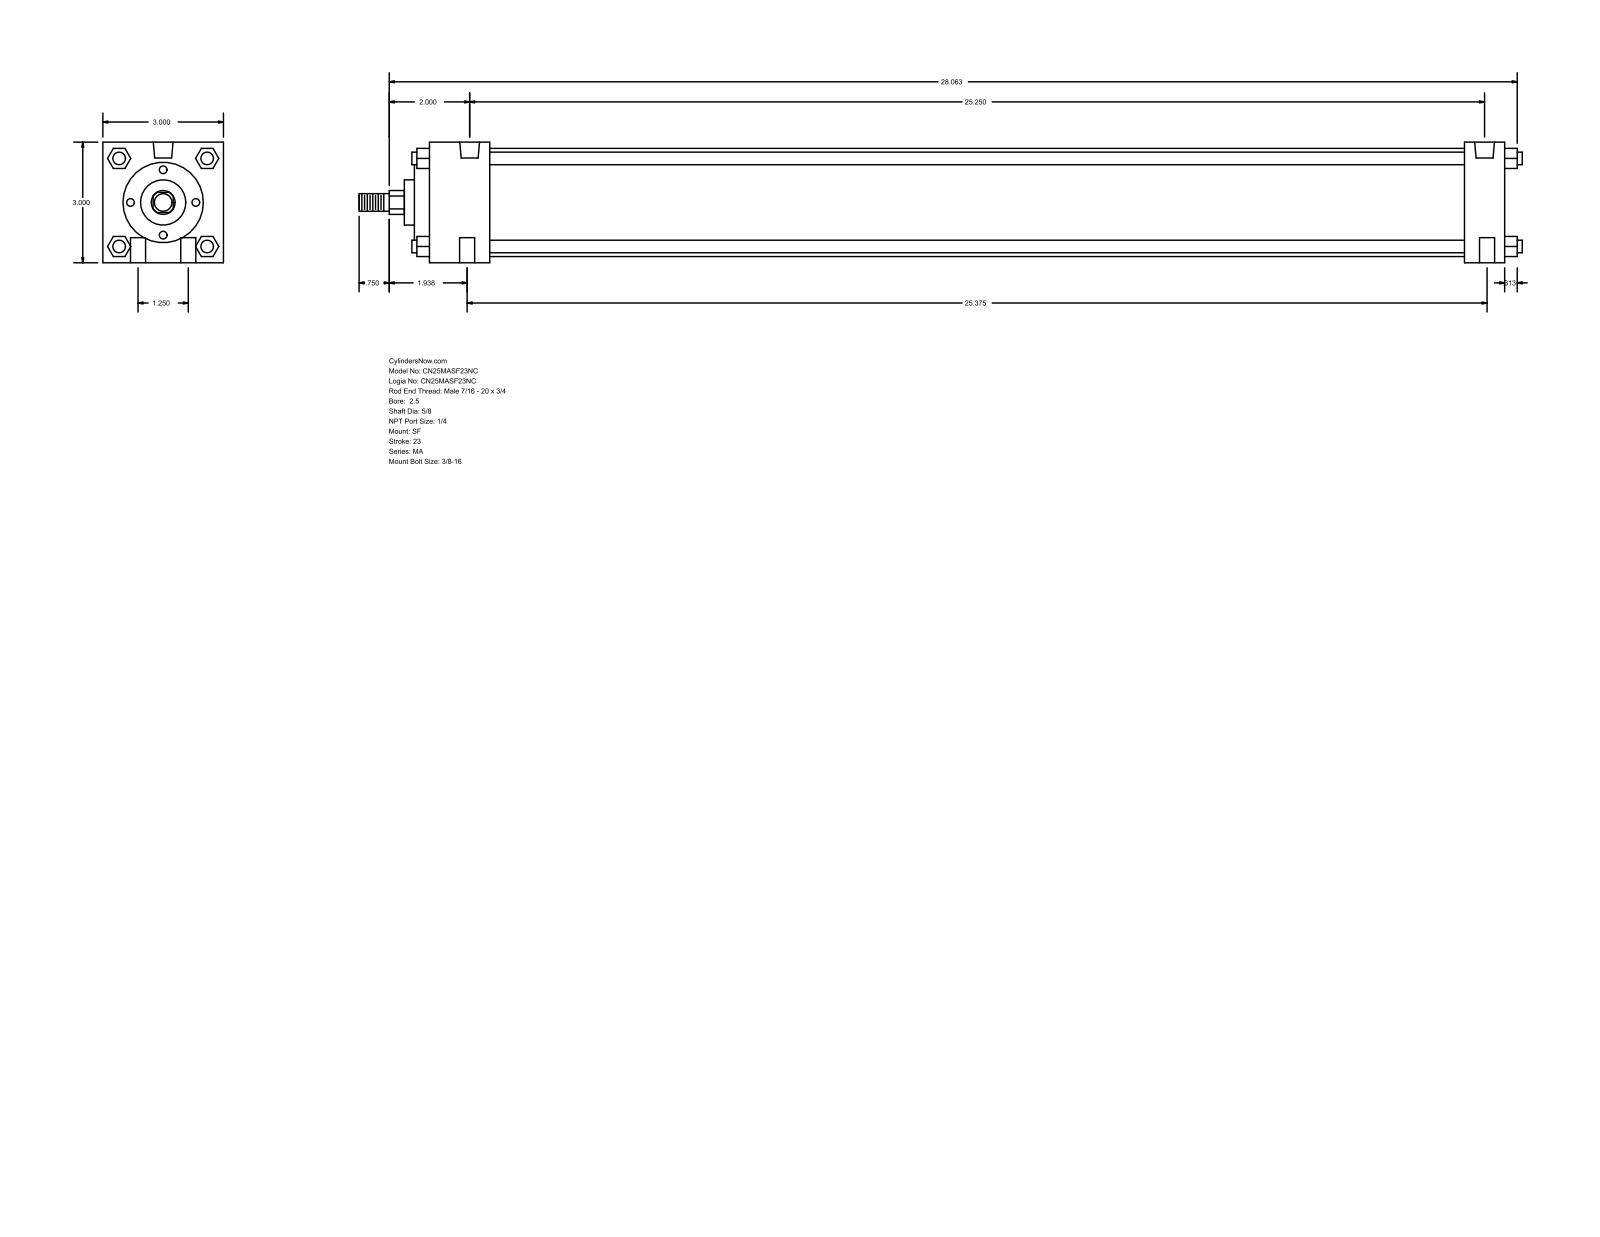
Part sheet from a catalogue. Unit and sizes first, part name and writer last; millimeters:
Units: millimetres
Overall size (bounding box): 735.01 × 76.2 × 76.2
Round holes (diameter × count): ⌀9.53 ×4, ⌀7.94 ×2, ⌀12.49 ×2
Round bosses / shafts (diameter × count): ⌀7.94 ×4, ⌀68.33 ×1, ⌀50.8 ×1, ⌀28.57 ×1, ⌀15.88 ×1, ⌀11.11 ×1
Partial cylindrical surfaces — rounded edges, fillets, slot ends (radius × count): R7.54 ×1
Main face-to-face distances: 76.2, 679.45, 25.4, 654.05, 38.1, 615.95, 641.35, 12.7, 9.52, 47.62
Hole centre spacings: 15.96, 643.14, 31.76, 641.35, 644.53, 645.31
Bodies: 0 solids, 126 faces (95 planar, 31 cylindrical, 0 other)
Part name (STEP PRODUCT): MA_SF__0250_0.625
STEP written by: GSSL Pune (CONFIG_CONTROL_DESIGN)
